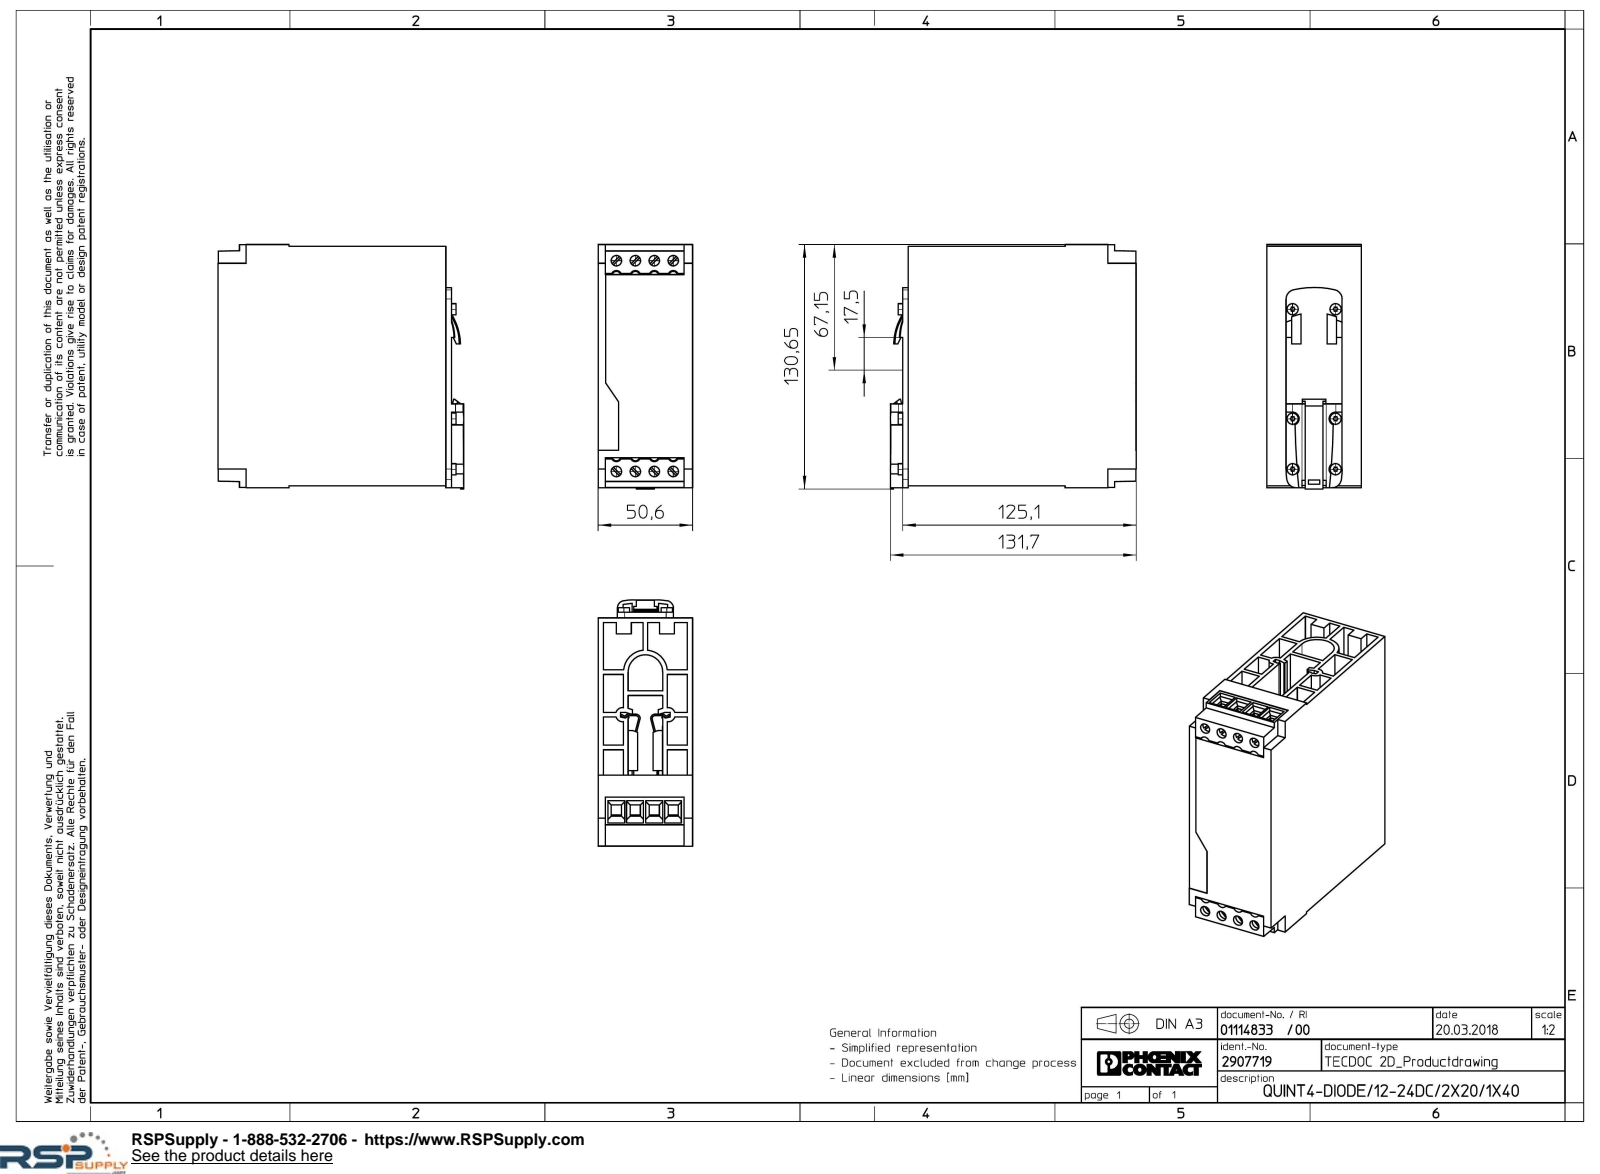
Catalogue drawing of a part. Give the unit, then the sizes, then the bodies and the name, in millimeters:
Units: millimetres
Overall size (bounding box): 131.7 × 130.65 × 50.6
Round holes (diameter × count): ⌀5.6 ×8
Round bosses / shafts (diameter × count): ⌀6 ×6
Partial cylindrical surfaces — rounded edges, fillets, slot ends (radius × count): R1.3 ×36, R2.75 ×8, R3.5 ×6, R5 ×4, R0.25 ×2, R0.5 ×2, R0.9 ×2, R1.35 ×2
Main face-to-face distances: 2.5, 2.8, 47.8, 50.6, 45, 13.55, 37.05, 10.75, 34.25, 16.05
Hole centre spacings: 10.16, 113.16, 20.32, 112.7, 114.52, 30.48, 116.75
Volume: 424 861 mm³ · Surface area: 153 755 mm²
Bodies: 1 solid, 570 faces (448 planar, 110 cylindrical, 12 other)
Part name (STEP PRODUCT): QUINT4_DIODE_12_24DC_2X20_1X40-select
STEP written by: Creo Elements/Direct Modeling 20.1A 29-Sep-2018 (C) Parametric Technology GmbH (AUTOMOTIVE_DESIGN)
